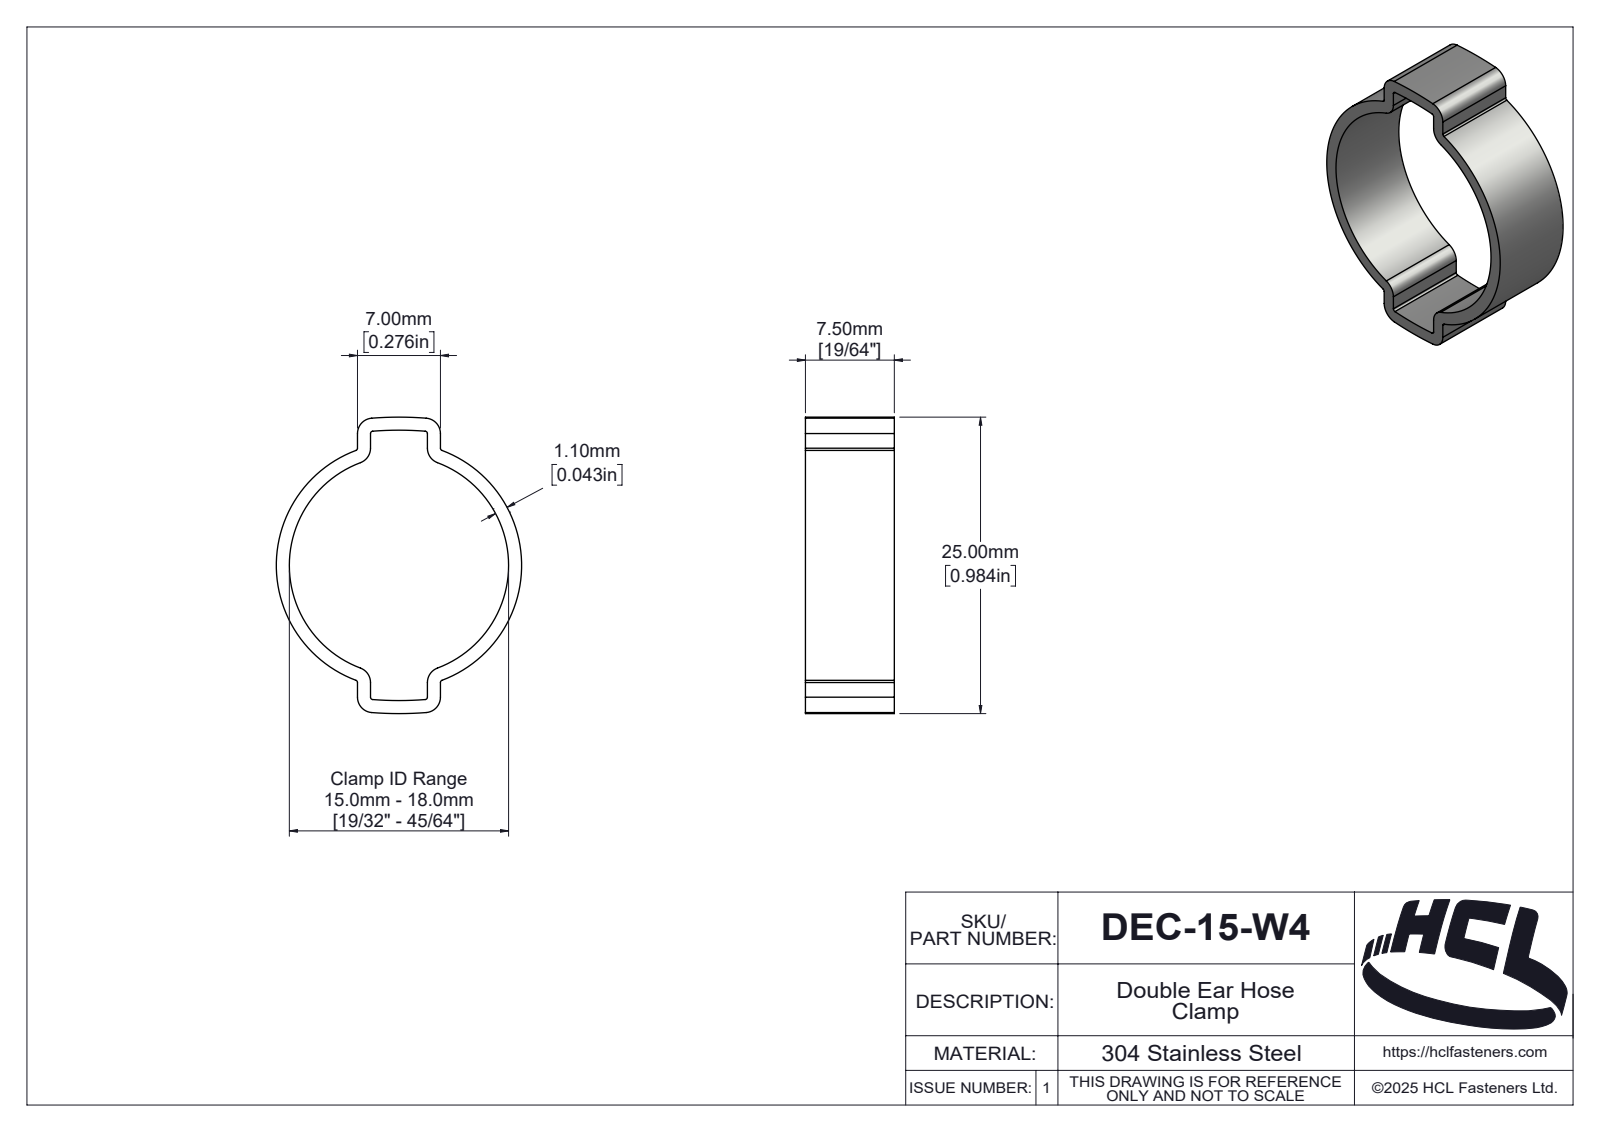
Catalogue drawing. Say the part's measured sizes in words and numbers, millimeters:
The part is named "DEC-15-W4". Its 3-D file was written by "SolidWorks 2025 (AUTOMOTIVE_DESIGN)". It is 1 solid with 137 faces: 12 planar, 67 cylindrical and 58 other. Overall it measures 25 by 20.7 by 7.5 millimeters. Its volume is 574 cubic millimeters and its surface area 1 201 square millimeters. Partial cylindrical surfaces (rounded edges, fillets, slot ends): 8 of radius 0.2, 8 of radius 1.3, 2 of radius 28.85, 2 of radius 29.95, 1 of radius 0.2, 1 of radius 0.81, 1 of radius 1.01, 1 of radius 1.06. The main face-to-face distances are 7.5, 1.1, 5.9, 7, 4.8, 3.38, 2.28, 2.52, 3.62, 3.23.
